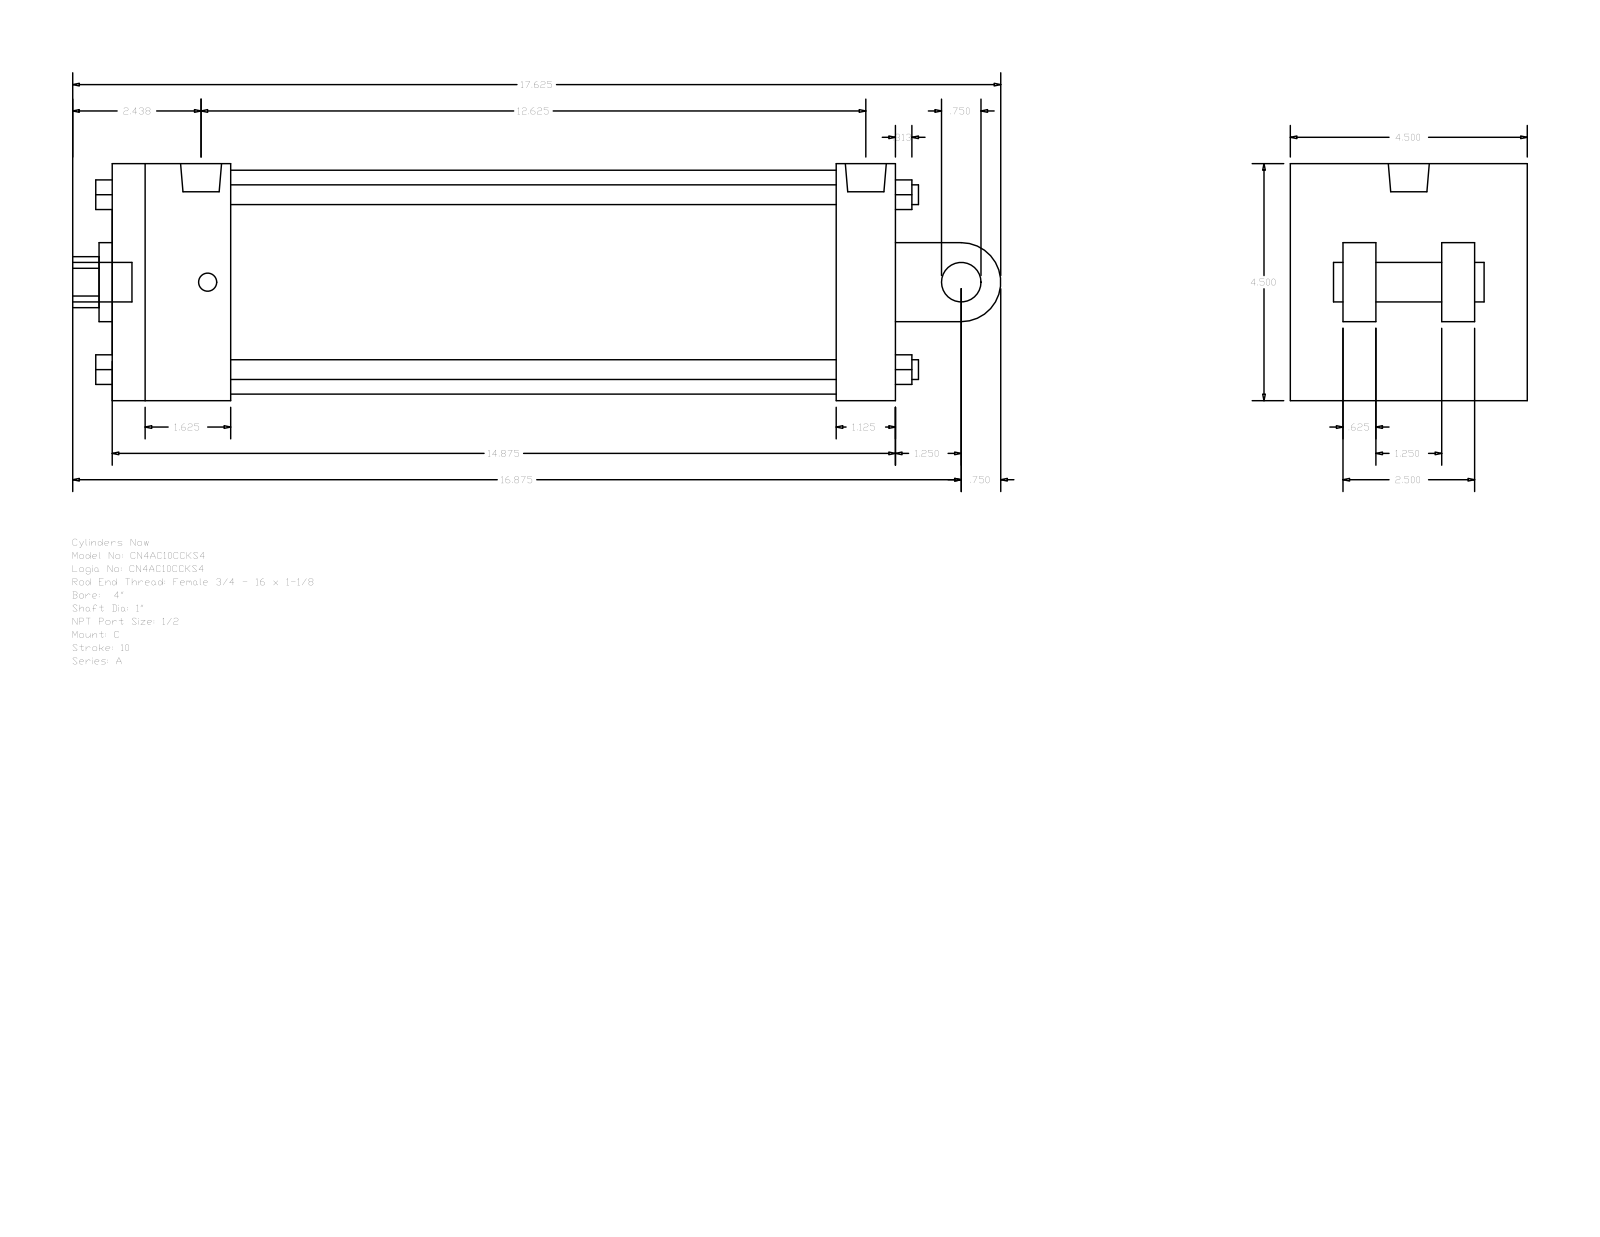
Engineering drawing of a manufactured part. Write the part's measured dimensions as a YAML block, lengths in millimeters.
part_name: "A_C__0400_1"
step_written_by: "GSSL Pune (CONFIG_CONTROL_DESIGN)"
units: millimeters
bodies: {solids: 0, faces: 135, planar: 102, cylindrical: 33, other: 0}
overall_size: [447.68, 114.3, 114.3]
round_holes:
  - {diameter: 8.73, count: 2}
  - {diameter: 19.77, count: 1}
  - {diameter: 25.4, count: 1}
  - {diameter: 38.1, count: 1}
  - {diameter: 107.95, count: 1}
round_bosses_or_shafts:
  - {diameter: 9.53, count: 4}
  - {diameter: 19.05, count: 2}
  - {diameter: 8.73, count: 2}
  - {diameter: 19.77, count: 1}
partial_cylinders:
  - {radius: 12.29, count: 1}
  - {radius: 19.05, count: 1}
face_to_face_distances: [114.3, 377.83, 73.03, 349.25, 28.58, 57.15, 292.1, 320.68, 15.87, 47.63]
hole_center_spacings: [3.18]
